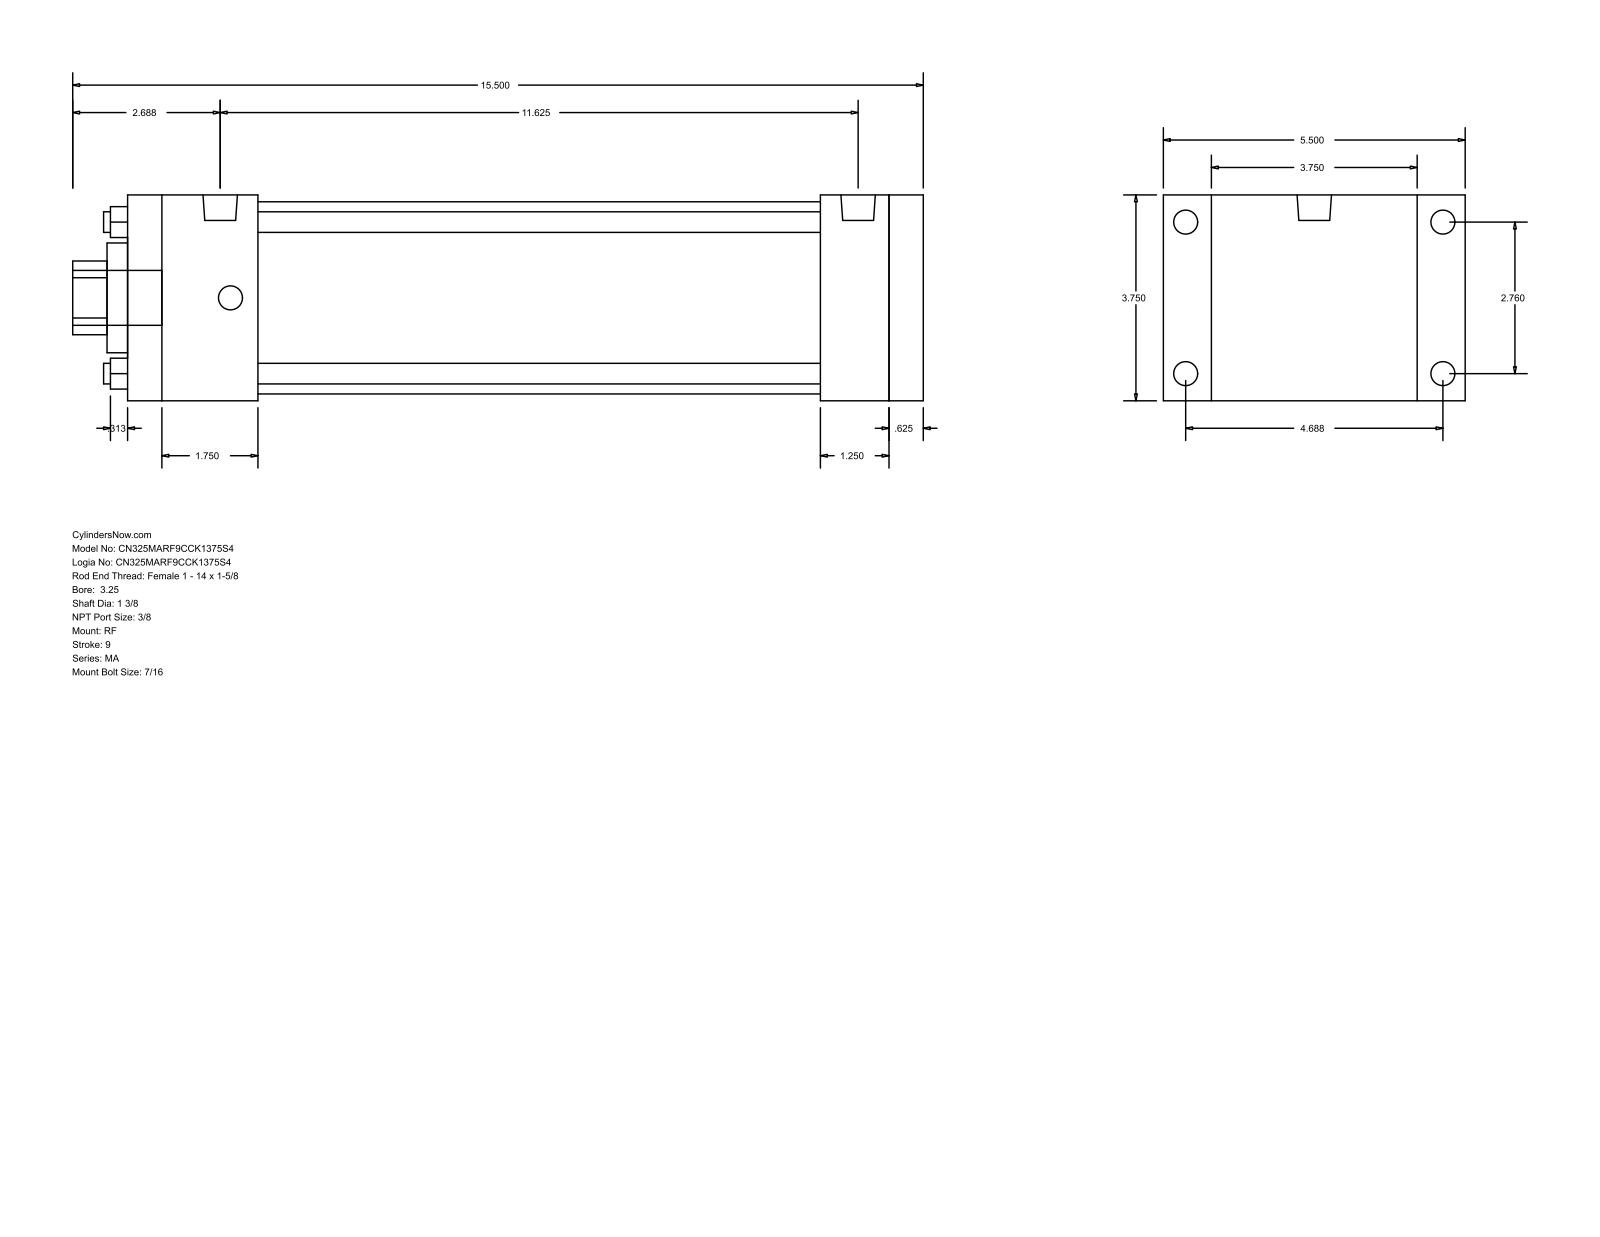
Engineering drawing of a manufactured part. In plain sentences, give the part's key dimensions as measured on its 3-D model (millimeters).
The part is named "MA_RF__0325_1.375". Its 3-D file was written by "GSSL Pune (CONFIG_CONTROL_DESIGN)". It is 0 solids with 92 faces: 64 planar, 28 cylindrical and 0 other. Overall it measures 393.7 by 139.7 by 95.25 millimeters. Round holes: 4 of diameter 9.53, 1 of diameter 34.92, 1 of diameter 50.8, 1 of diameter 88.9. Round bosses or shafts: 8 of diameter 11.11, 2 of diameter 15.93, 1 of diameter 25.4. Partial cylindrical surfaces (rounded edges, fillets, slot ends): 1 of radius 17.06. The main face-to-face distances are 95.24, 368.3, 15.88, 352.42, 22.23, 117.47, 320.67, 31.75, 47.63, 60.32. The hole center spacings are 49.57, 70.1, 99.14.
